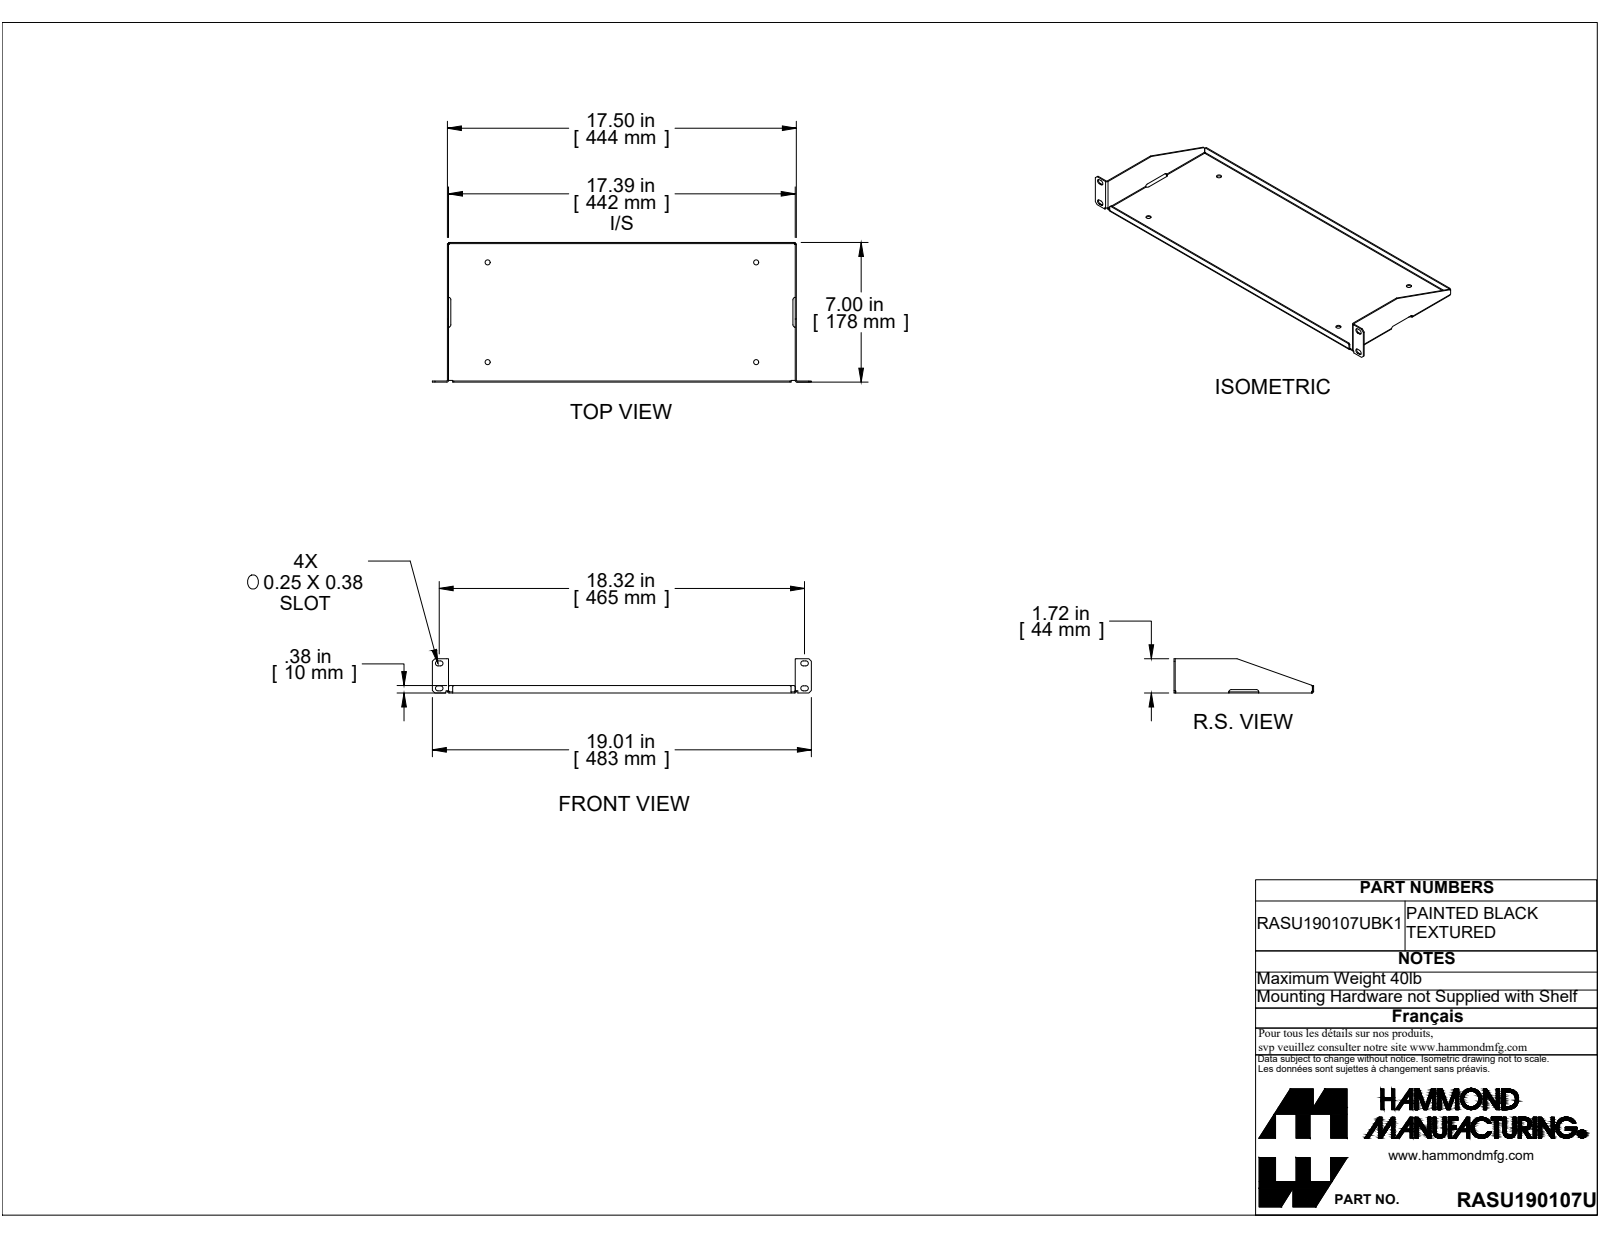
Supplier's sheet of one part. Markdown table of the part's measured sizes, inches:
| quantity | value |
| --- | --- |
| part name | RASU190107UBK1_REV1 |
| STEP written by | SolidWorks 2021 (AUTOMOTIVE_DESIGN) |
| units | inches |
| bodies | 1 solid, 103 faces (67 planar, 36 cylindrical, 0 other) |
| overall size | 19.022 × 7 × 1.718 |
| volume | 8.648 in³ |
| surface area | 307.1 in² |
| round holes (diameter × count) | 0.25 × 4 |
| partial cylindrical surfaces (radius × count) | 0.125 × 15, 0.086 × 6, 0.029 × 4, 0.029 × 2 |
| main face-to-face distances | 0.057, 17.463, 6.943, 17.406, 17.52, 6.886, 7, 0.319, 0.376, 1.342 |
| hole center spacings | 5, 13.468, 14.366 |
